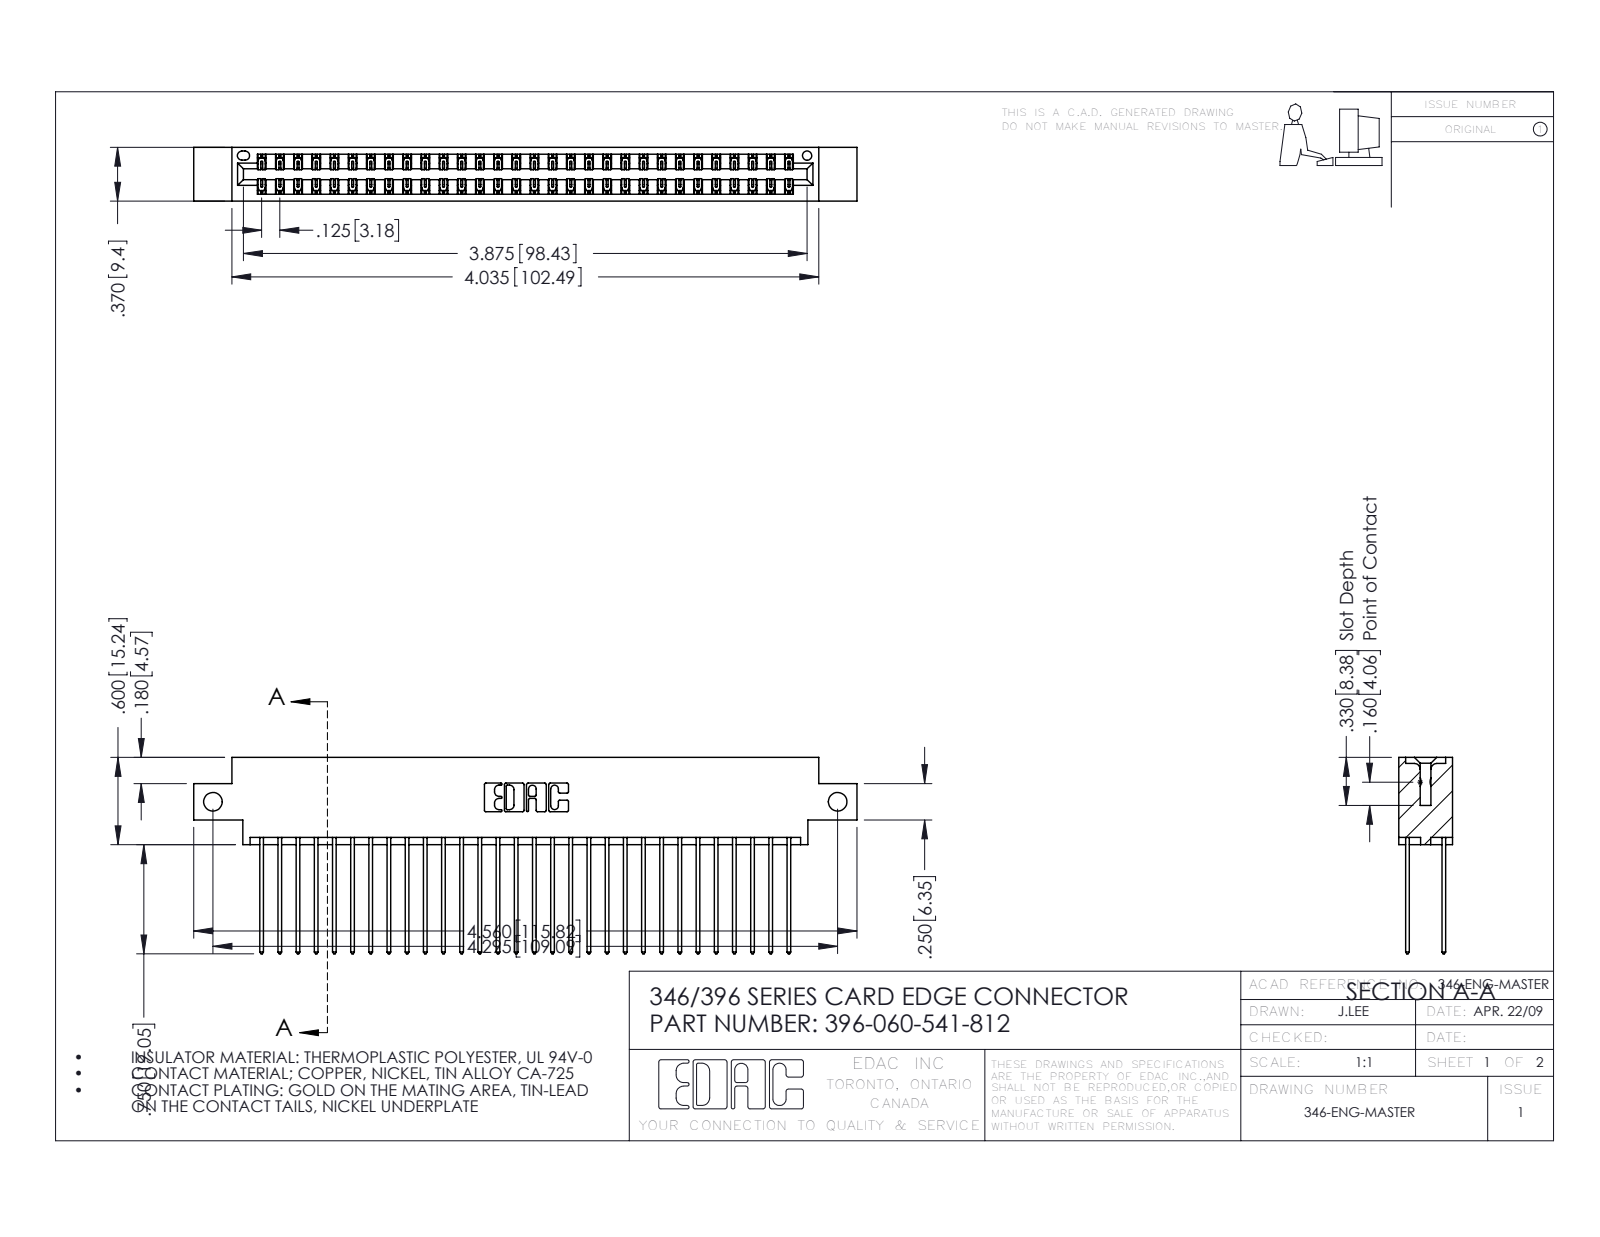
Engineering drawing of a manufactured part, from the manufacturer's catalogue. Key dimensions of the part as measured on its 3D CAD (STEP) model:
Part name (STEP PRODUCT): 346 Part_0.170 Offset - Side Mount; 345-292-001_345-293-141; 396-060-541-812
STEP written by: SolidWorks 2016 (CONFIG_CONTROL_DESIGN)
Units: inches
Bodies: 61 solids, 3246 faces (2180 planar, 1066 cylindrical, 0 other)
Overall size (bounding box): 4.56 × 1.35 × 0.37
Volume: 0.69 in³ · Surface area: 26.41 in²
Round holes (diameter × count): ⌀0.128 ×2, ⌀0.064 ×1
Partial cylindrical surfaces — rounded edges, fillets, slot ends (radius × count): R0.006 ×90, R0.01 ×60, R0.01 ×22, R0.007 ×6, R0.031 ×6, R0.026 ×3, R0.014 ×2, R0.022 ×2
Main face-to-face distances: 0.048, 0.322, 0.25, 0.072, 0.298, 0.025, 0.37, 0.275, 0.225, 0.148
Hole centre spacings: 4.295
